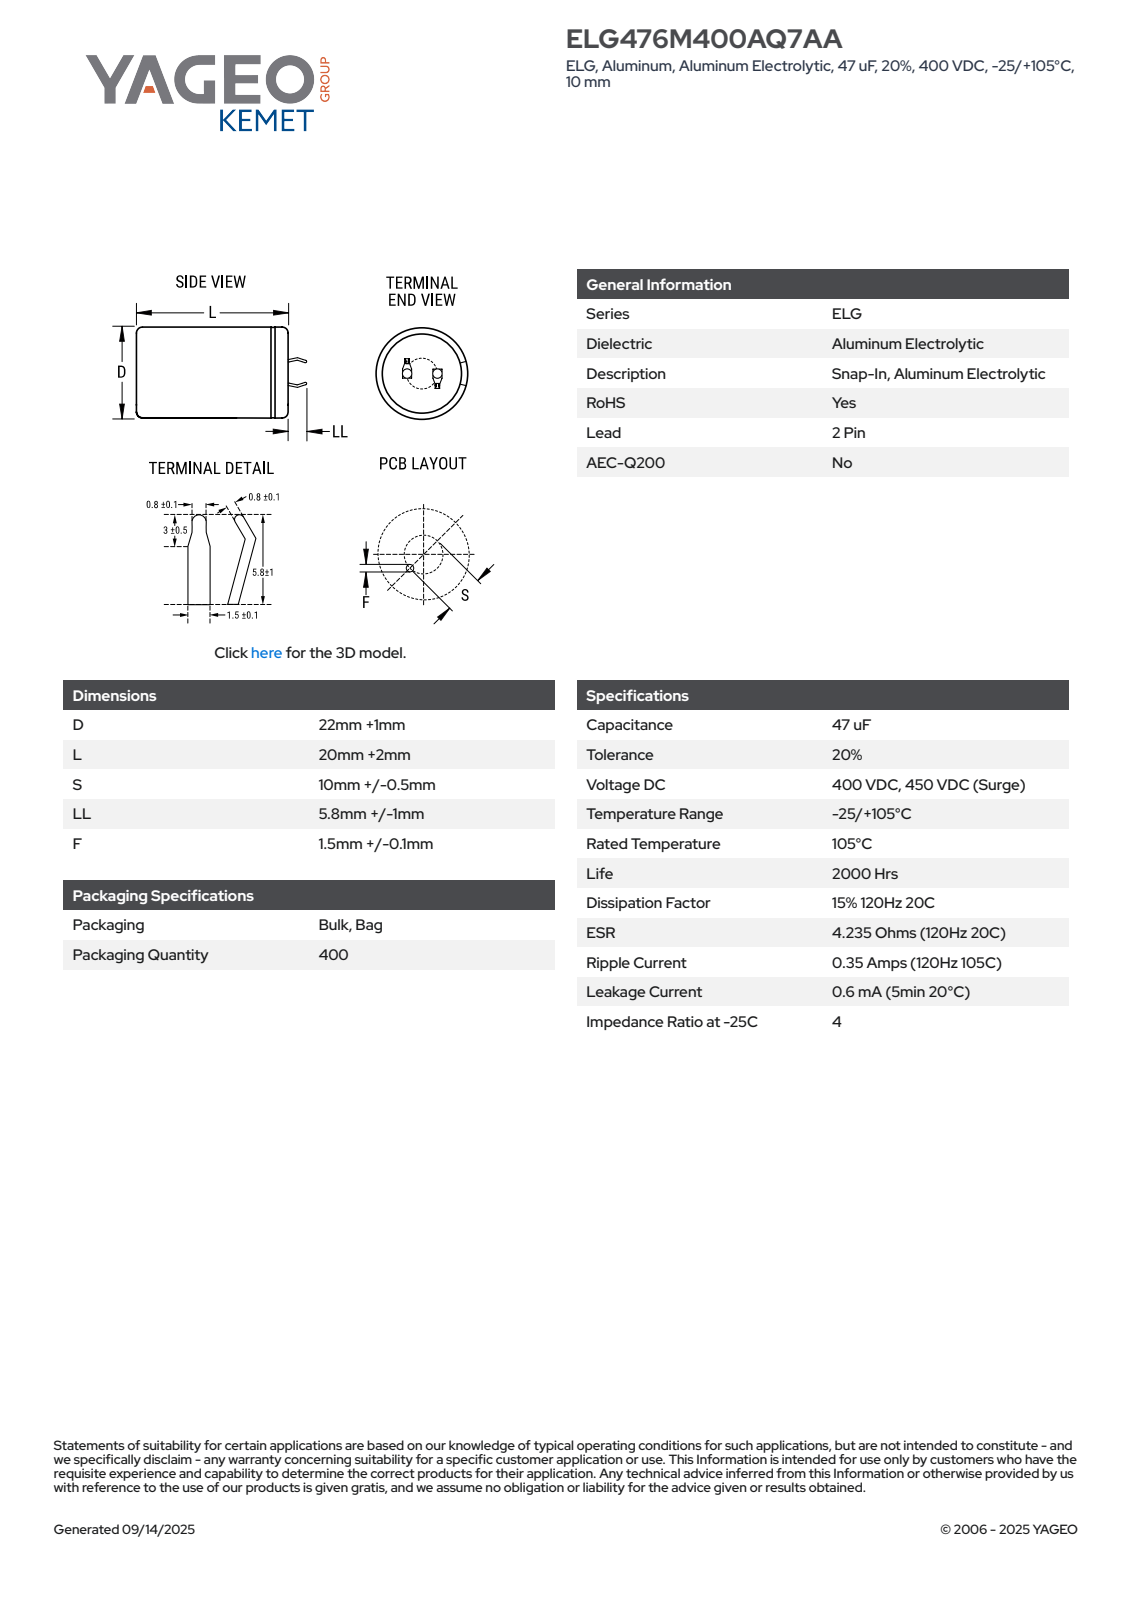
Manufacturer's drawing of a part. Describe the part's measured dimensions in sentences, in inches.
The part is named "CARS_K2P_22X20_D23L22S10LL6.8F1.6". Its 3-D file was written by "SolidWorks 2014 (AUTOMOTIVE_DESIGN)". It is 1 solid with 100 faces: 52 planar, 9 cylindrical and 39 other. Overall it measures 1.133 by 0.906 by 0.906 inches. Its volume is 0.55 cubic inches and its surface area 3.79 square inches. Round holes: 1 of diameter 0.801. Round bosses or shafts: 1 of diameter 0.906. Partial cylindrical surfaces (rounded edges, fillets, slot ends): 1 of radius 0.452. The main face-to-face distances are 0.866, 0.024, 0.885, 0.02, 0.279, 0.3, 0.03, 0.053, 0.302, 0.255.
